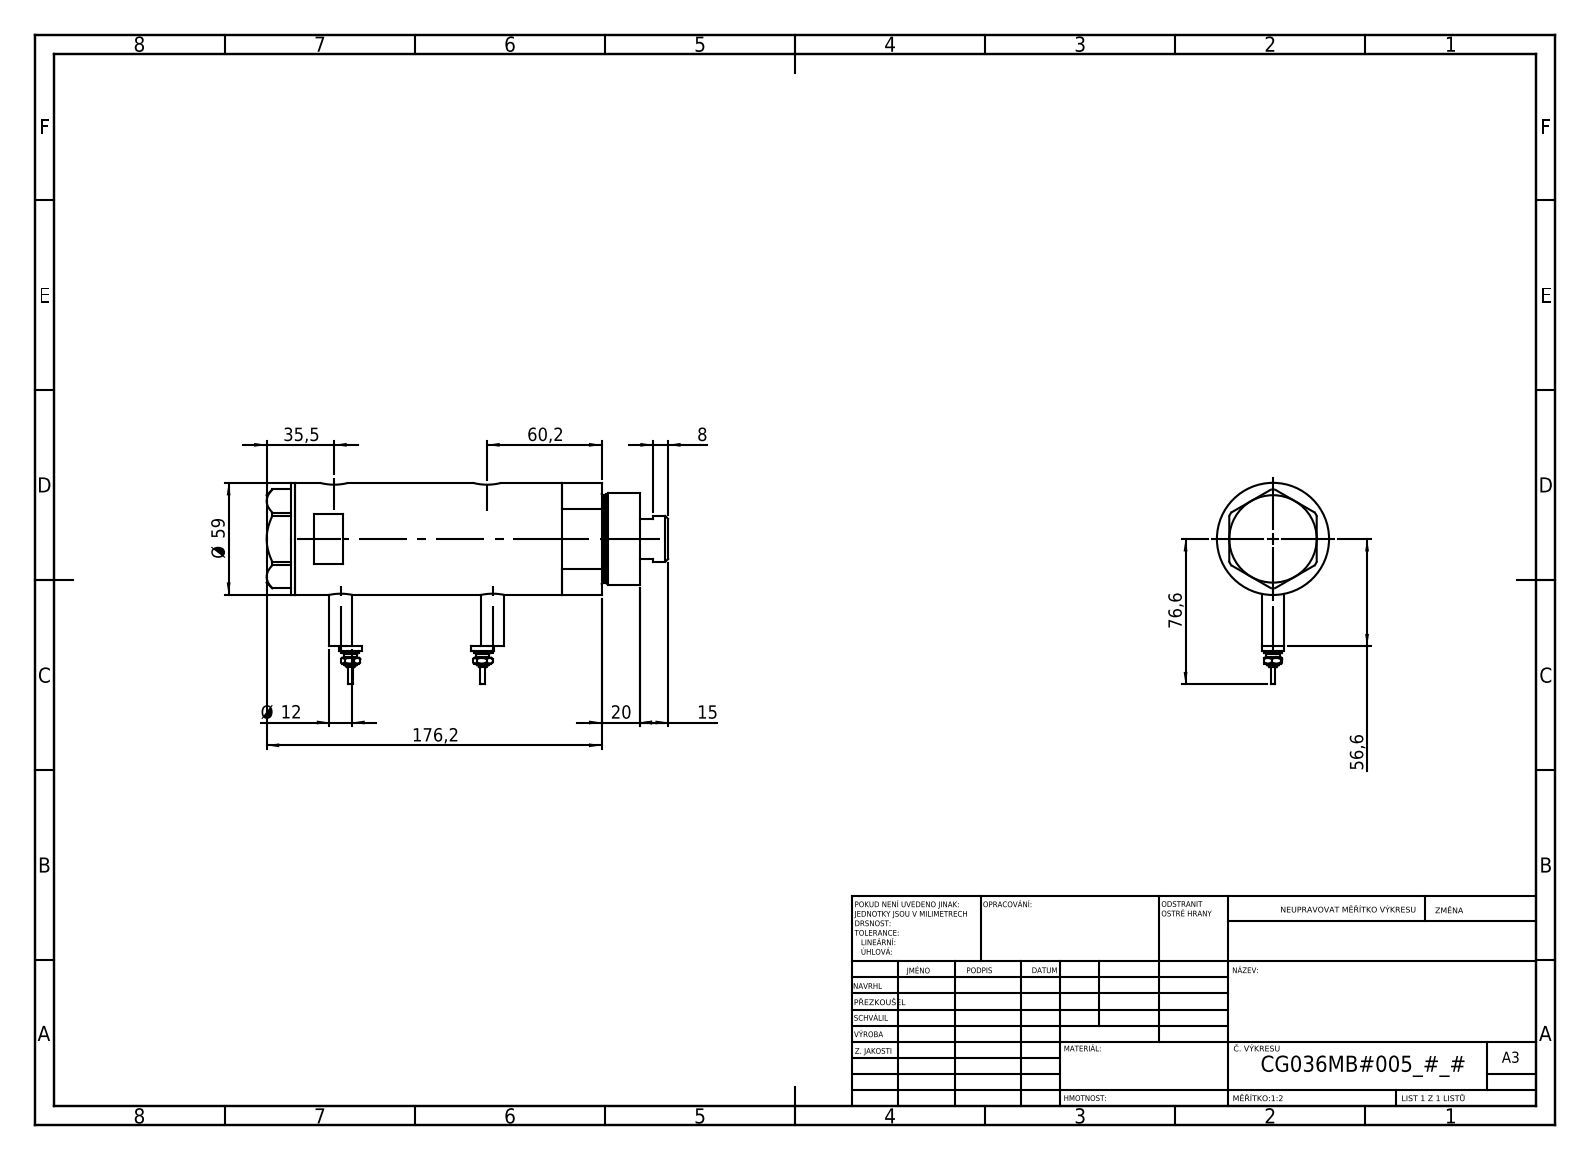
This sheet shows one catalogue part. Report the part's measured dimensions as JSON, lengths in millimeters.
{"part_name": "Switch; V270CG_FRONT; V270CG_VC; V270CG_BACK (+1 more)", "step_written_by": "SolidWorks 2019 (CONFIG_CONTROL_DESIGN)", "units": "millimeters", "bodies": {"solids": 6, "faces": 212, "planar": 79, "cylindrical": 69, "other": 64}, "overall_size": [211.2, 106.1, 59], "volume_mm3": 508173, "surface_area_mm2": 104308, "round_holes": [[9.73, 2], [12.5, 2], [15, 2], [8.5, 1], [25, 1], [26.5, 1], [36, 1], [40, 1], [52, 1]], "round_bosses_or_shafts": [[12, 4], [9, 2], [7, 2], [4.5, 2], [2.5, 2], [59, 1], [48, 1], [46, 1]], "face_to_face_distances": [102.2, 23.5, 78.7, 15, 38.5, 117.2, 2, 196.2, 181.2, 157.7], "hole_center_spacings": [2.9, 3.5, 77, 79.9, 80.5, 83.4]}
